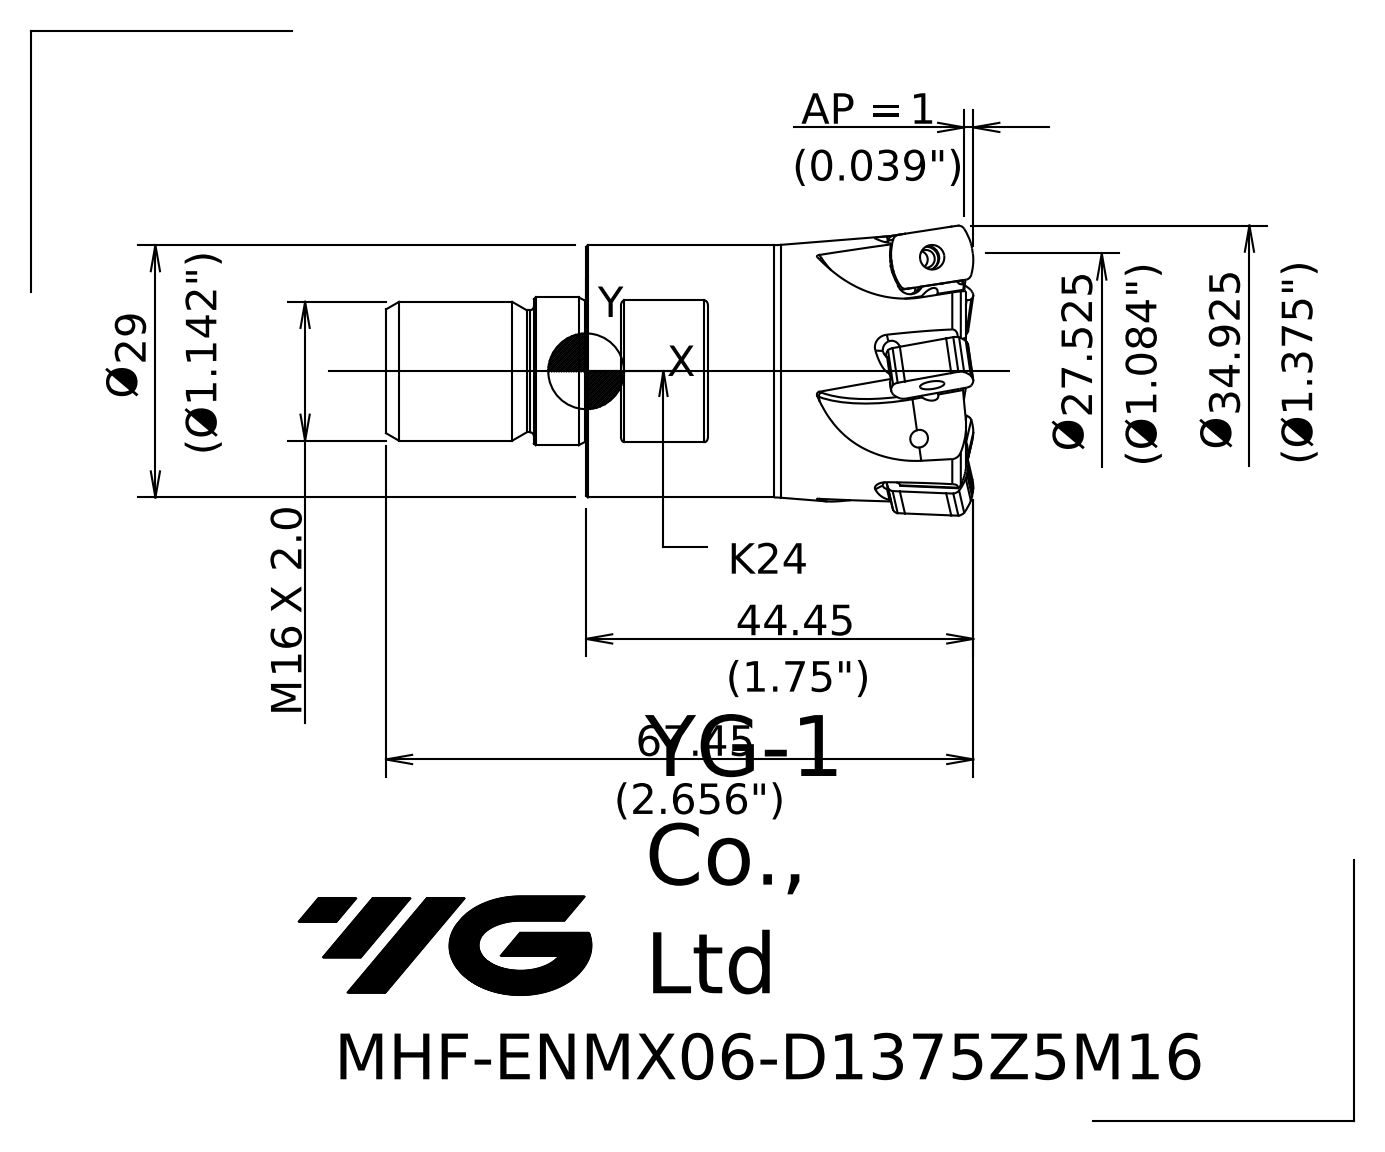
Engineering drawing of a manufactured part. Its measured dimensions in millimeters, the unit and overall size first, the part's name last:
Units: millimetres
Overall size (bounding box): 67.45 × 34.96 × 34.96
Round holes (diameter × count): ⌀1.6 ×1, ⌀5 ×1
Round bosses / shafts (diameter × count): ⌀29 ×1, ⌀17 ×1, ⌀15.96 ×1, ⌀14 ×1
Partial cylindrical surfaces — rounded edges, fillets, slot ends (radius × count): R0.4 ×4
Main face-to-face distances: 43.25, 24, 66.25, 23, 10, 0.4, 43.65, 66.65, 29.65, 29.25
Volume: 33 304 mm³ · Surface area: 9 914 mm²
Bodies: 1 solid, 103 faces (11 planar, 10 cylindrical, 82 other)
Part name (STEP PRODUCT): 10222F54F831lo8f
STEP written by: SIEMENS PLM Software NX 10.0 (AP203_CONFIGURATION_CONTROLLED_3D_DESIGN_OF_MECHANICAL_PARTS_AND_ASSEMBLIES_MIM_LF)
